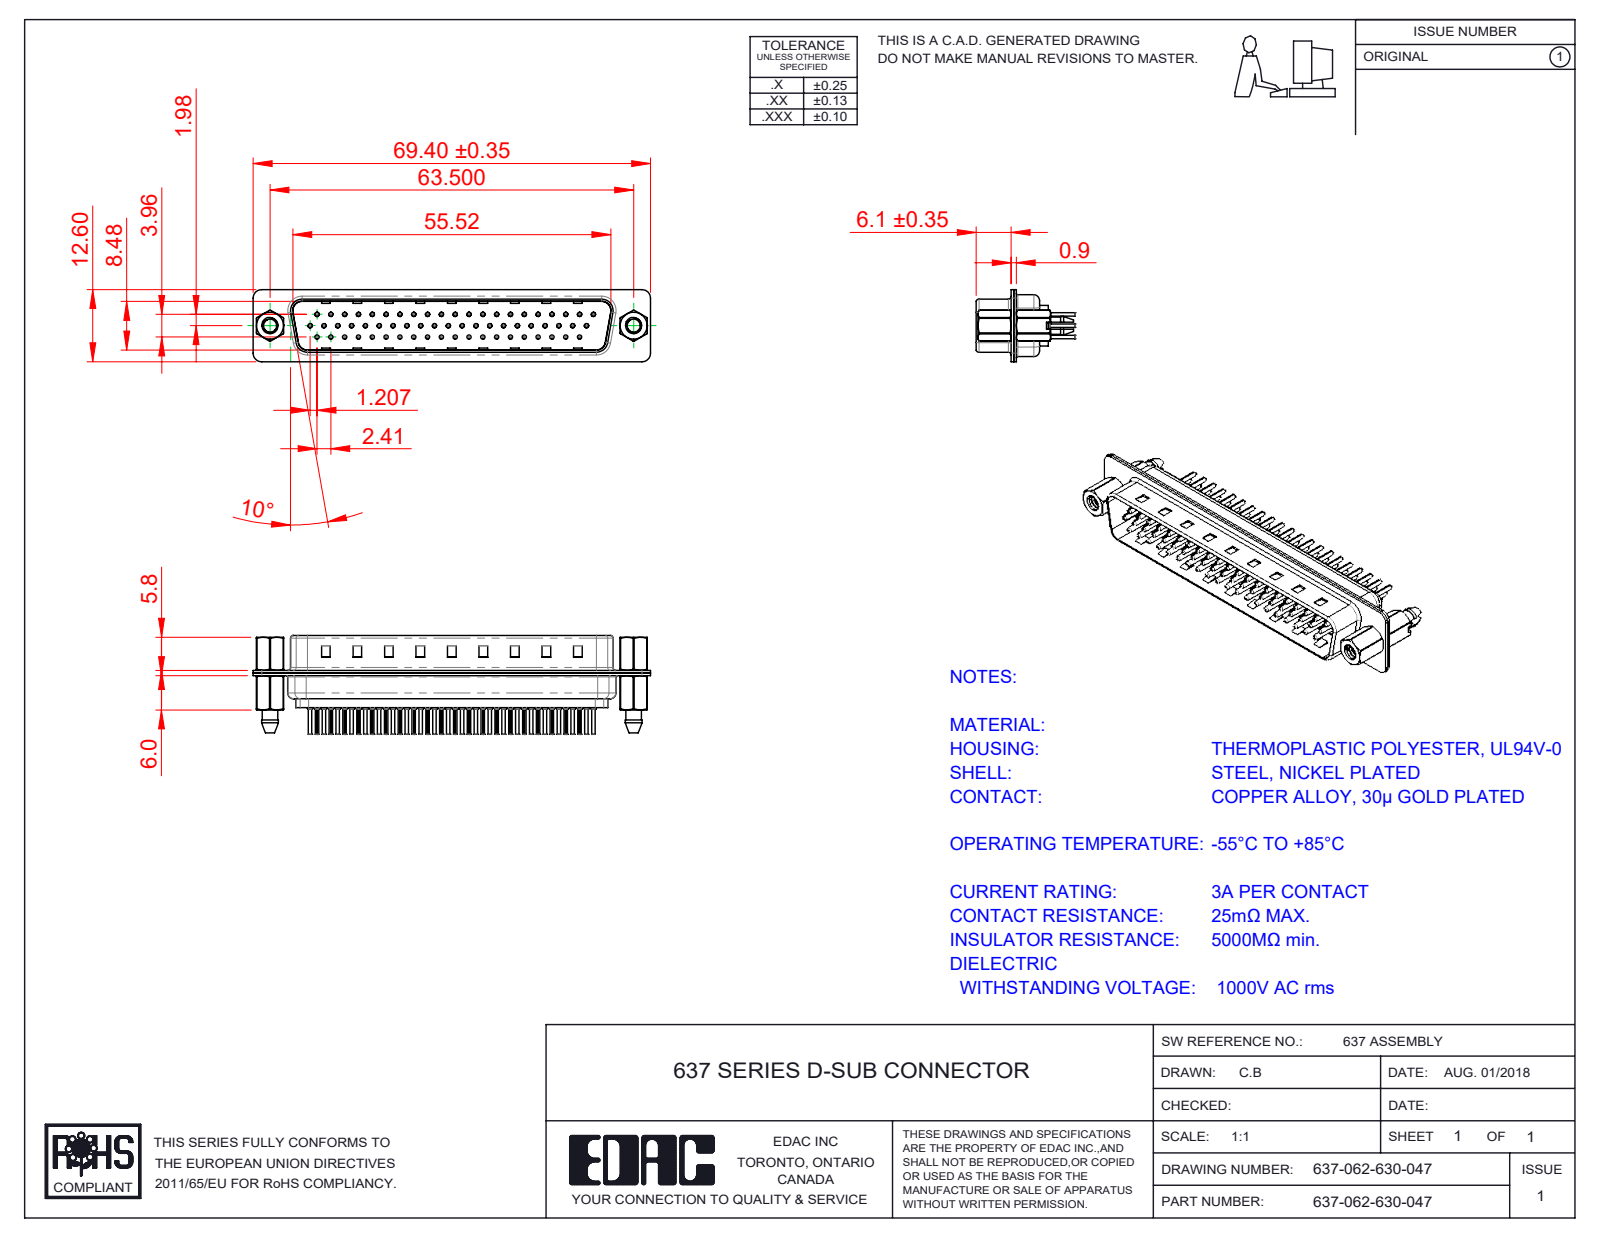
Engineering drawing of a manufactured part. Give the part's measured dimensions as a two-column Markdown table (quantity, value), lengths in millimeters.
| quantity | value |
| --- | --- |
| part name | 637 Housing_62 Contacts; 637 Contact Row 1_30; 637 4-40 Threaded Boardlock_LP; 637 Shell Front_62 Contacts (+5 more) |
| STEP written by | SolidWorks 2020 (CONFIG_CONTROL_DESIGN) |
| units | millimeters |
| bodies | 69 solids, 6812 faces (1745 planar, 2539 cylindrical, 2528 other) |
| overall size | 69.4 × 17.25 × 12.6 |
| volume | 4 014 mm³ |
| surface area | 14 391 mm² |
| round holes (diameter × count) | 0.2 × 62, 0.35 × 62, 1.1 × 62, 1.6 × 62, 2.26 × 2, 2.29 × 2, 4 × 2, 4.8 × 2 |
| round bosses / shafts (diameter × count) | 2 × 62, 1.5 × 62, 0.75 × 62, 0.6 × 62, 4.9 × 2, 2.79 × 2 |
| partial cylindrical surfaces (radius × count) | 0.1 × 124, 1.5 × 18, 2 × 12, 0.5 × 8, 1.6 × 6, 0.25 × 4, 0.55 × 4, 0.7 × 4 |
| main face-to-face distances | 0.45, 0.4, 0.7, 8.88, 8.48, 9.64, 0.9, 0.31, 0.76, 1.16 |
| hole center spacings | 7.24, 2.32, 2.41, 4.13, 9.65, 4.83, 14.48, 11.04 |
